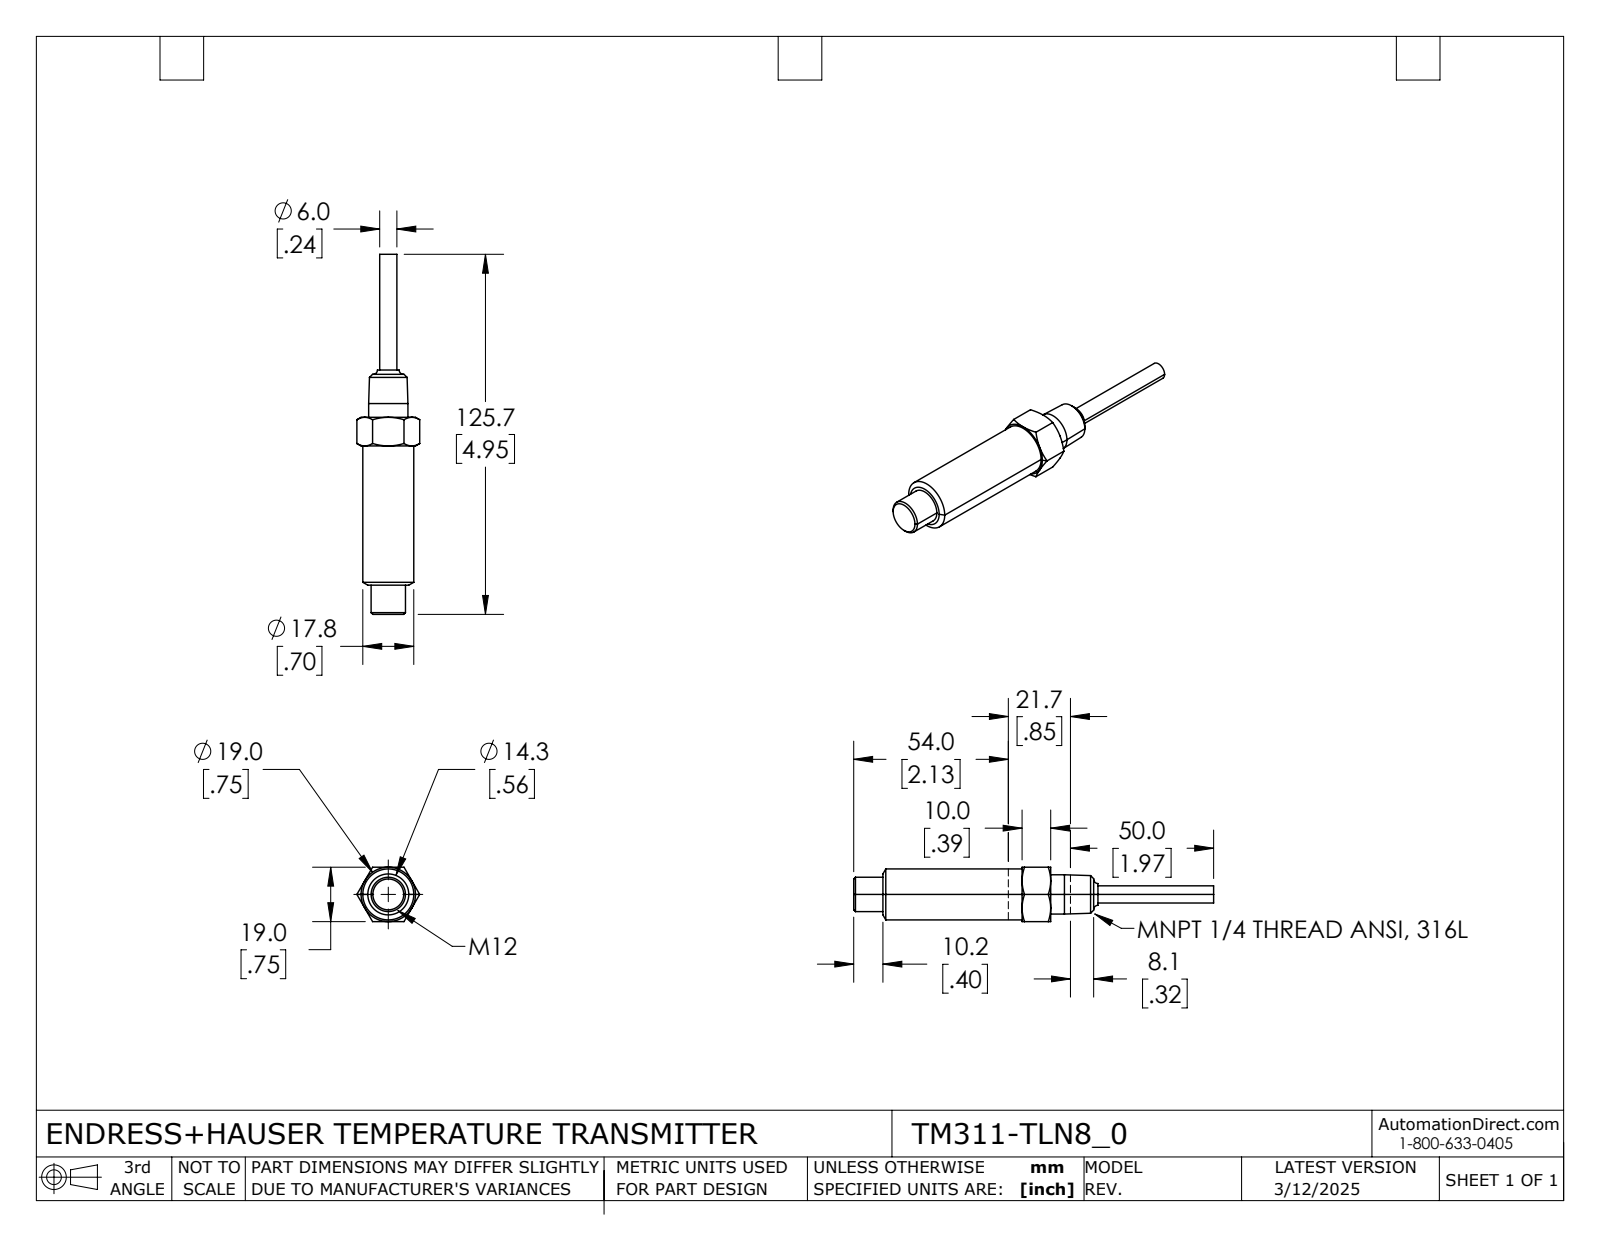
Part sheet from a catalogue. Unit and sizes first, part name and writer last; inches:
Units: inches
Overall size (bounding box): 4.949 × 0.864 × 0.748
Round bosses / shafts (diameter × count): ⌀0.701 ×1, ⌀0.54 ×1, ⌀0.472 ×1, ⌀0.236 ×1
Main face-to-face distances: 0.748, 2.709, 2.307, 0.402, 0.394, 1.913, 2.315, 2.24, 2.634, 4.547
Volume: 1.199 in³ · Surface area: 8.804 in²
Bodies: 1 solid, 47 faces (13 planar, 8 cylindrical, 26 other)
Part name (STEP PRODUCT): TM311-TLN8_0
STEP written by: SolidWorks 2021 (AUTOMOTIVE_DESIGN)
